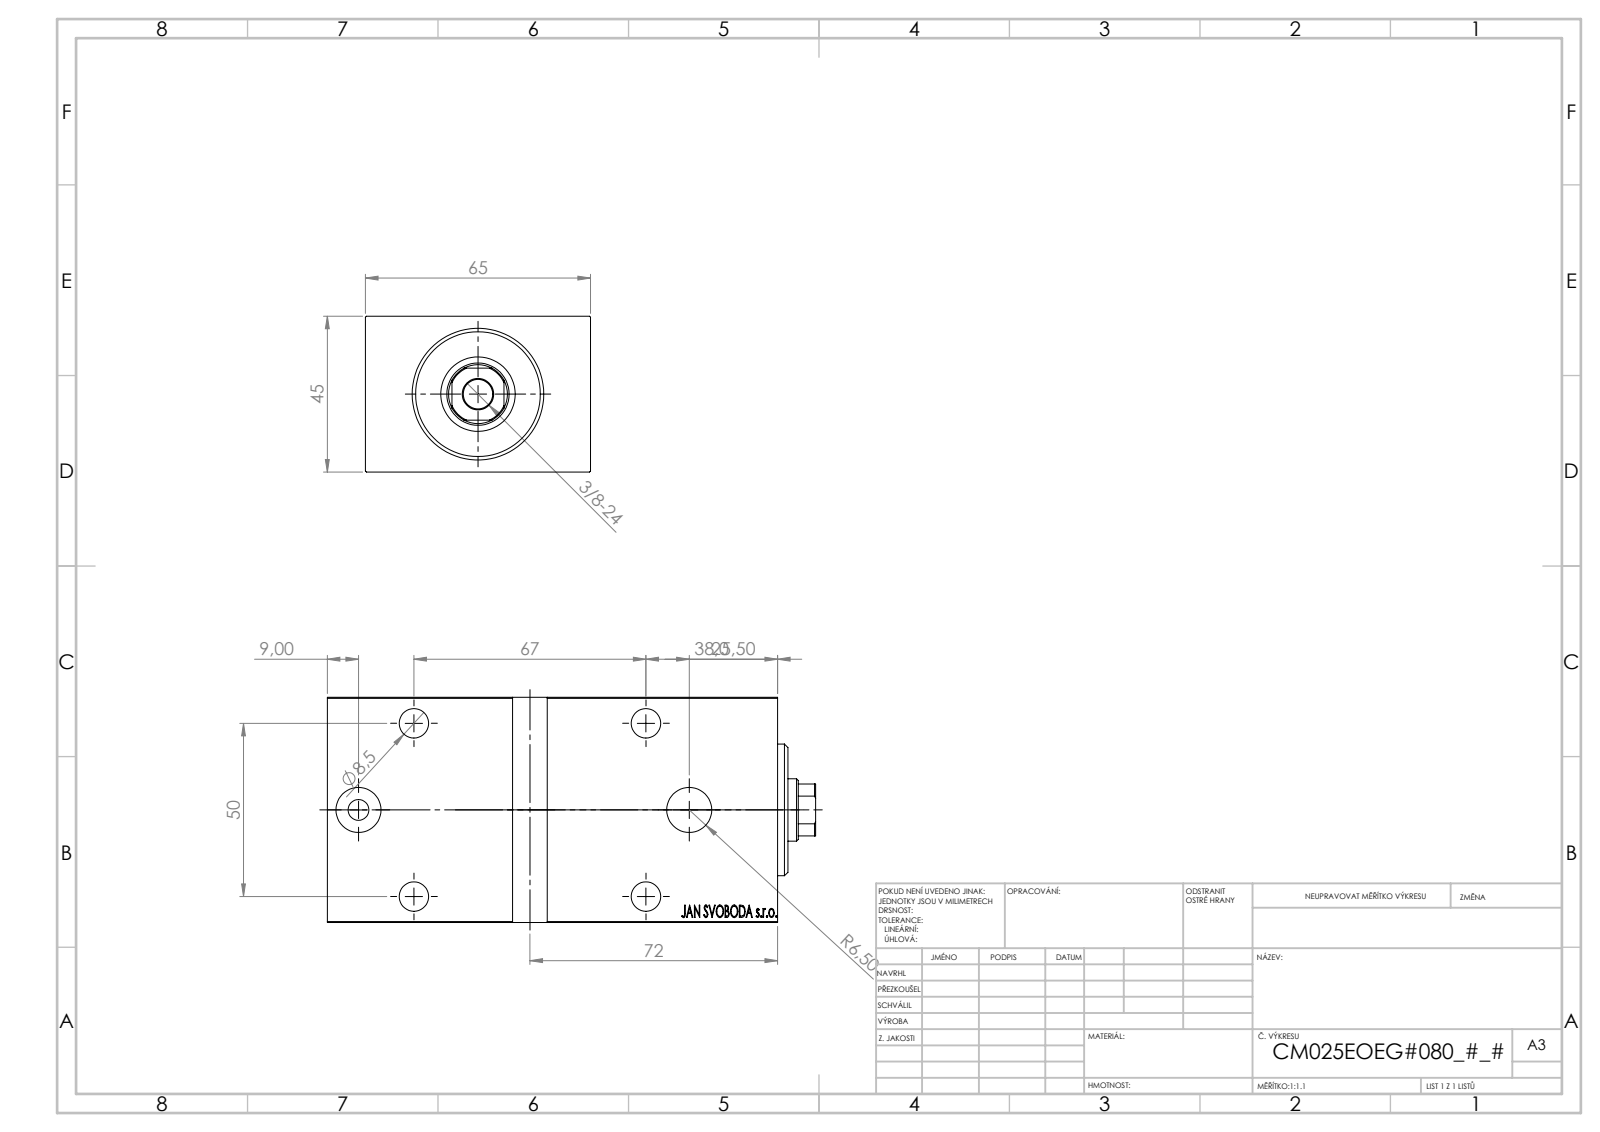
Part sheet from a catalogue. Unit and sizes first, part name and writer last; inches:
Units: inches
Overall size (bounding box): 5.551 × 2.559 × 1.772
Round holes (diameter × count): ⌀0.335 ×5, ⌀0.531 ×4, ⌀0.512 ×2, ⌀0.709 ×1, ⌀0.846 ×1, ⌀0.984 ×1, ⌀1.378 ×1
Round bosses / shafts (diameter × count): ⌀1.496 ×1, ⌀1.063 ×1, ⌀0.236 ×1
Partial cylindrical surfaces — rounded edges, fillets, slot ends (radius × count): R0.335 ×1
Main face-to-face distances: 1.772, 2.559, 5.118, 0.236, 4.882, 0.197, 4.921, 4.685, 0.315, 0.118
Hole centre spacings: 1.1, 1.169, 1.969, 2.638, 3.281, 3.291, 3.413, 3.76
Volume: 21.46 in³ · Surface area: 99.47 in²
Bodies: 3 solids, 849 faces (409 planar, 46 cylindrical, 394 other)
Part name (STEP PRODUCT): V450CM_E_VCP; V450CM_VC_B; V450CM_E_Body
STEP written by: SolidWorks 2019 (CONFIG_CONTROL_DESIGN)
